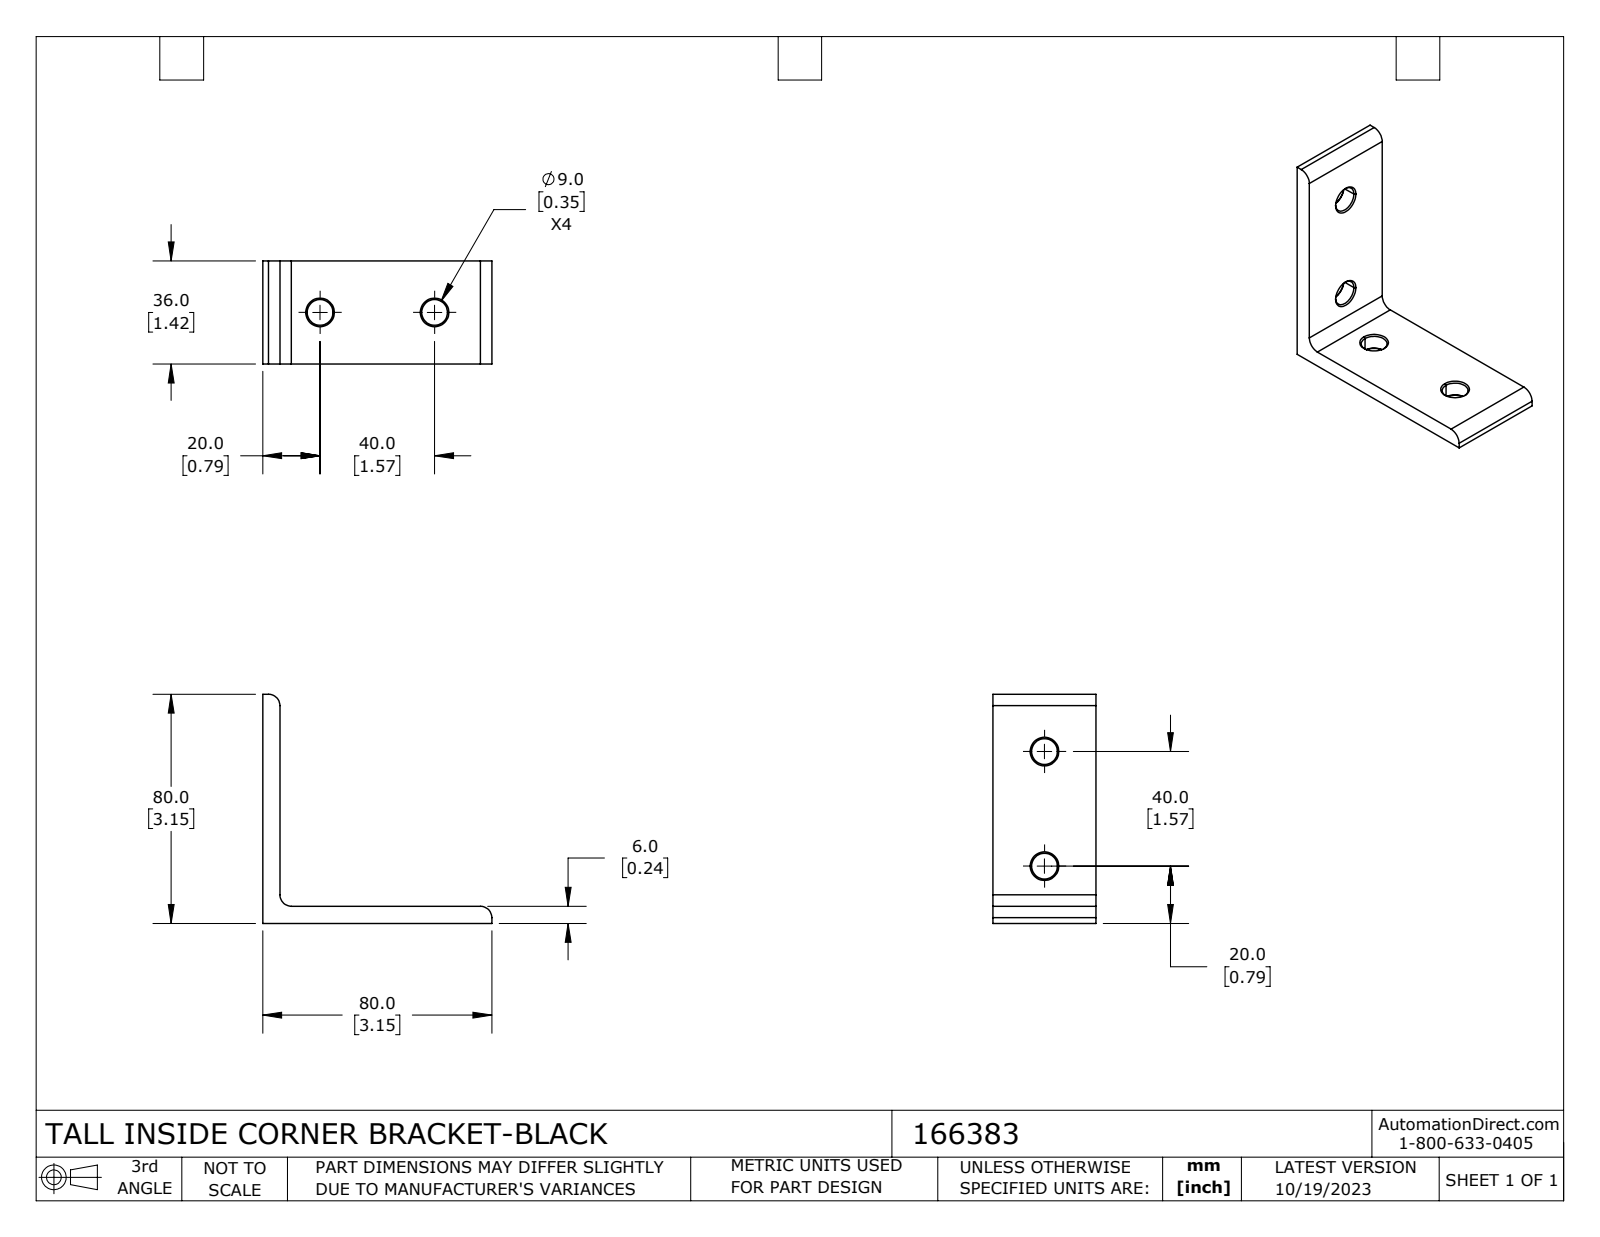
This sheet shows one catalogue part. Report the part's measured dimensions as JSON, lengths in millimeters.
{"part_name": "166383", "step_written_by": "SolidWorks 2023 (CONFIG_CONTROL_DESIGN)", "units": "millimeters", "bodies": {"solids": 1, "faces": 35, "planar": 8, "cylindrical": 11, "other": 16}, "overall_size": [80, 80, 36], "volume_mm3": 31584, "surface_area_mm2": 13282, "round_holes": [[9, 4]], "partial_cylinders_radius": [[4, 3]], "face_to_face_distances": [6, 36, 80, 74], "hole_center_spacings": [40]}
